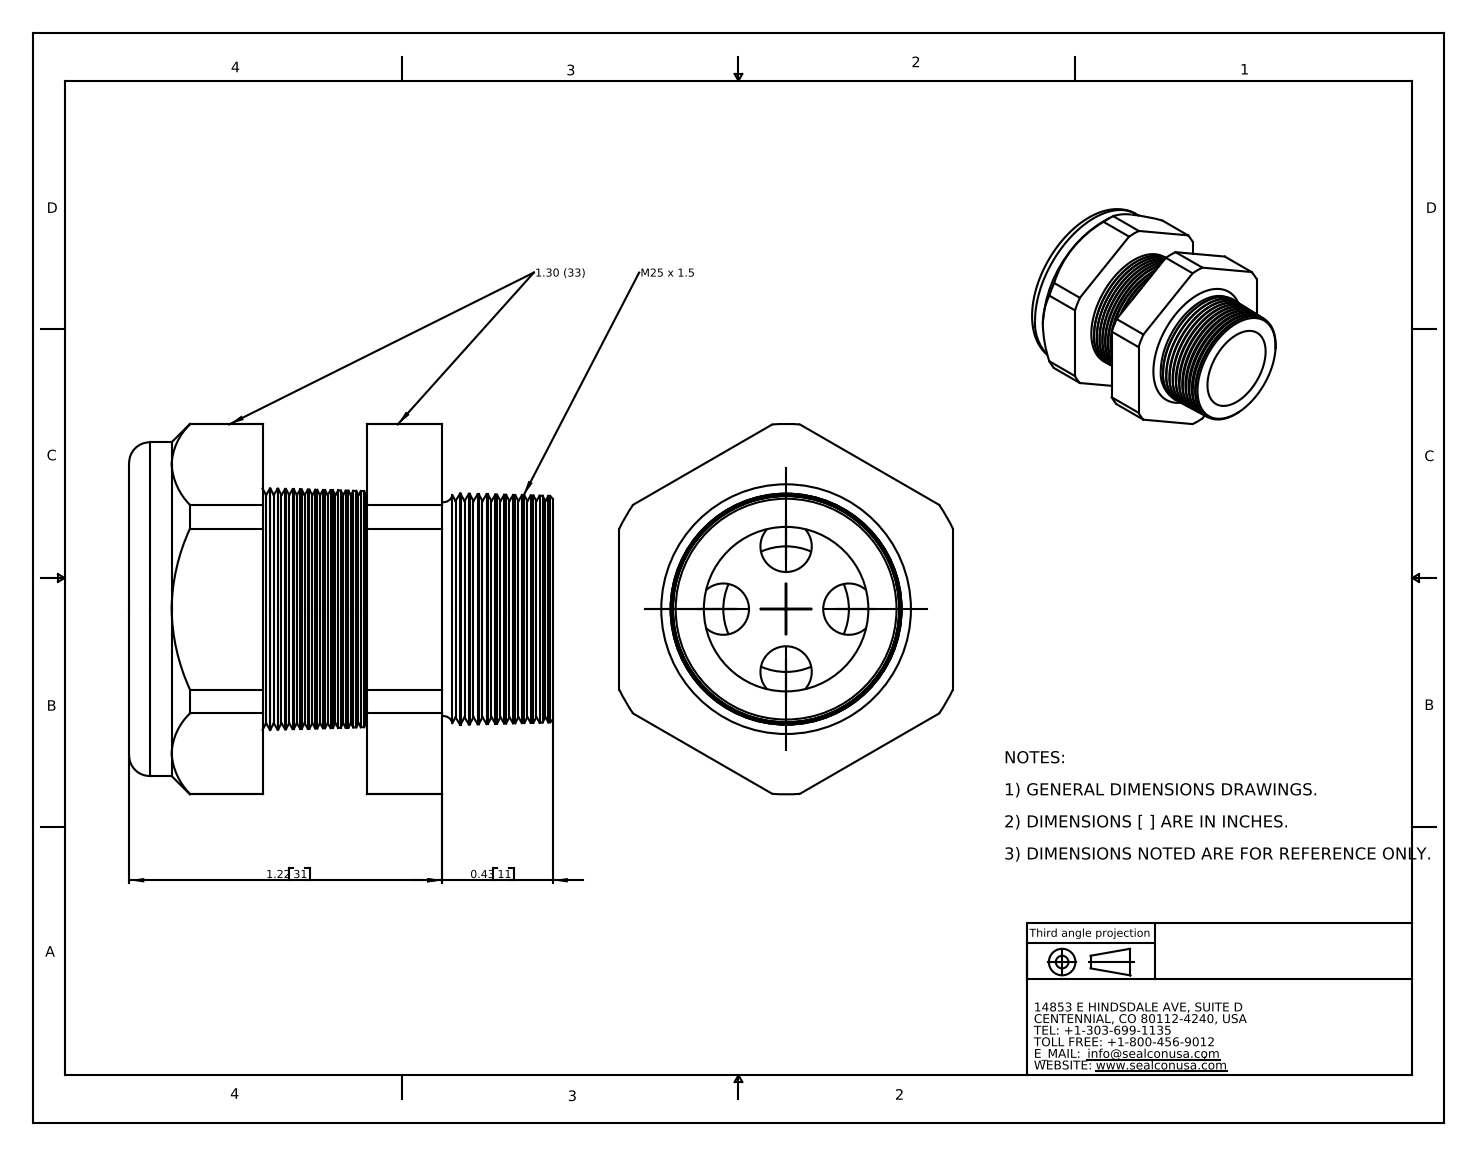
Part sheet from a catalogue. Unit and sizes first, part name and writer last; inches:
Units: inches
Overall size (bounding box): 1.65 × 1.443 × 1.3
Round holes (diameter × count): ⌀0.2 ×4, ⌀0.69 ×1, ⌀0.71 ×1
Round bosses / shafts (diameter × count): ⌀1.3 ×1
Partial cylindrical surfaces — rounded edges, fillets, slot ends (radius × count): R0.721 ×1
Main face-to-face distances: 1.3, 0.405, 0.7, 0.295, 0.52, 0.925, 1.22, 0.35, 0.17, 0.575
Hole centre spacings: 0.244, 0.346, 0.489
Volume: 1.15 in³ · Surface area: 17.13 in²
Bodies: 2 solids, 214 faces (20 planar, 28 cylindrical, 166 other)
Part name (STEP PRODUCT): CD25M6-BK
STEP written by: SolidWorks 2007 (CONFIG_CONTROL_DESIGN)
